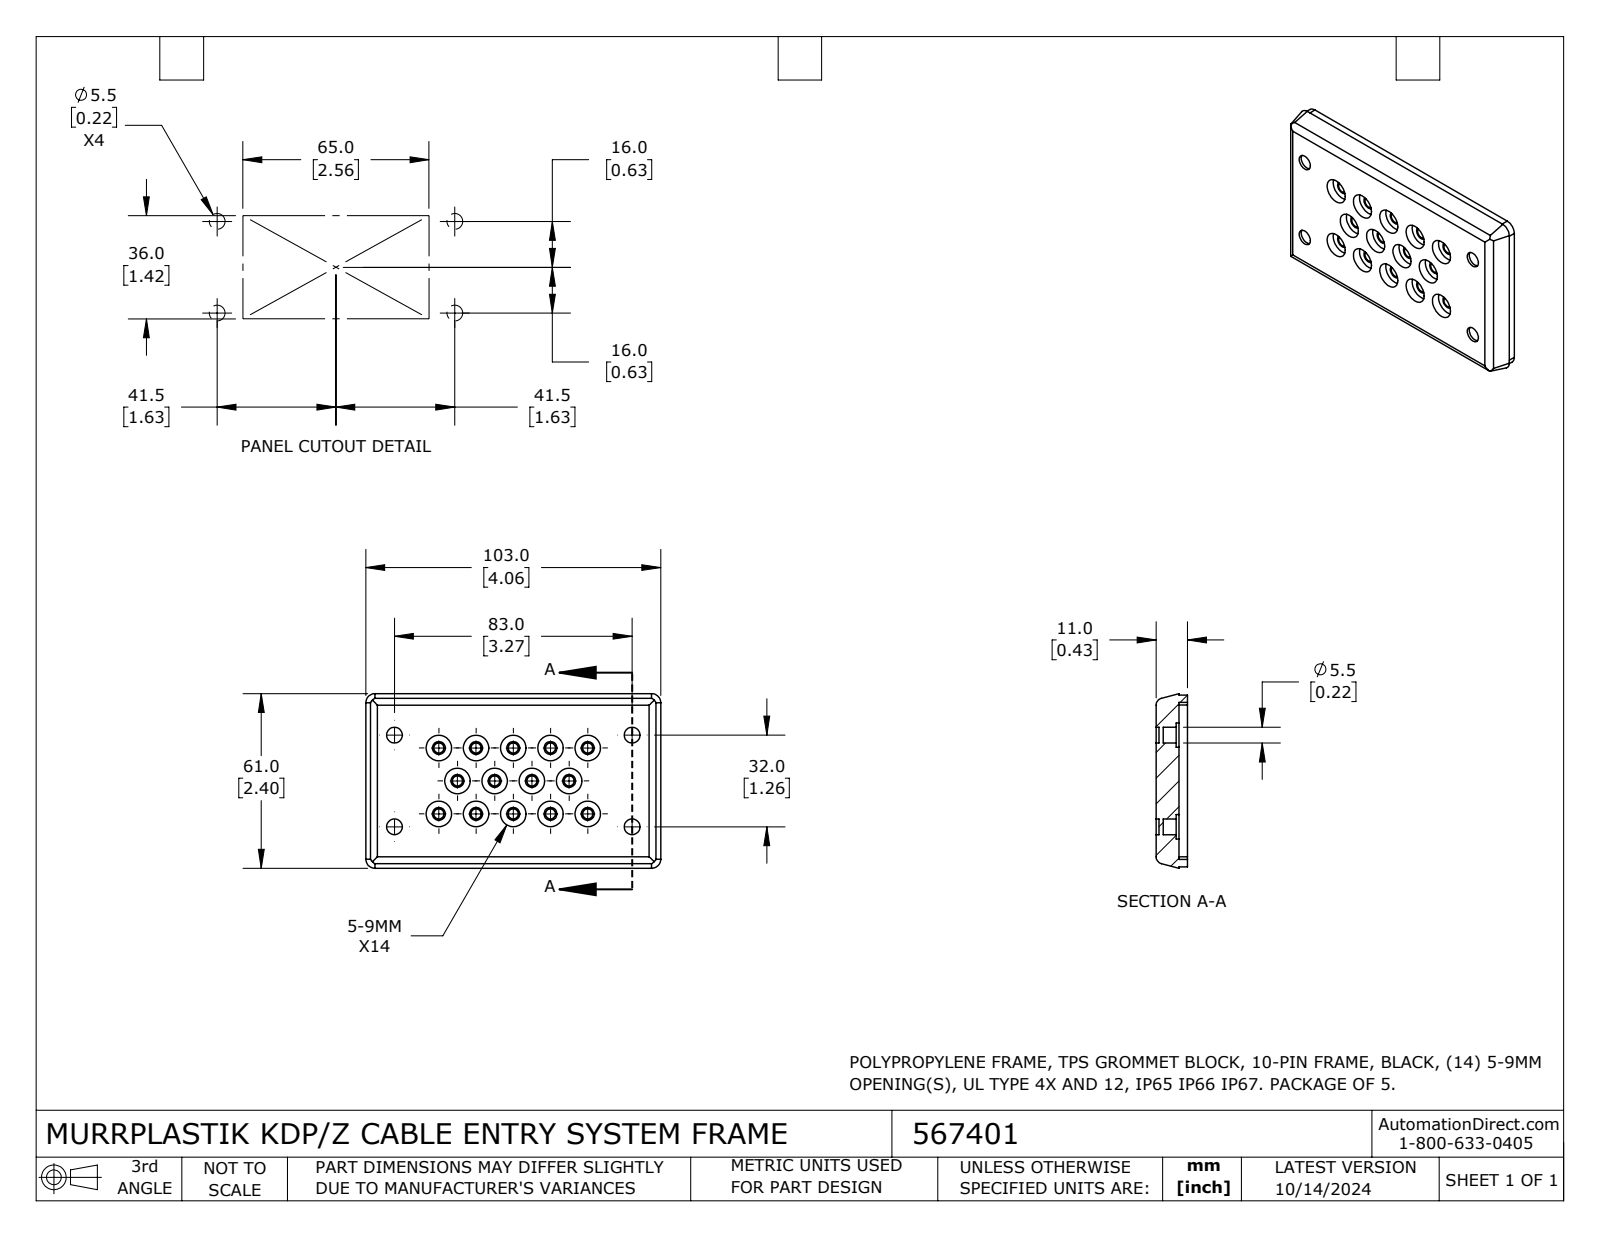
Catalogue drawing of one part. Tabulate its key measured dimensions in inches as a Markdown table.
| quantity | value |
| --- | --- |
| part name | 567401 |
| STEP written by | SolidWorks 2023 (CONFIG_CONTROL_DESIGN) |
| units | inches |
| bodies | 1 solid, 226 faces (84 planar, 138 cylindrical, 4 other) |
| overall size | 4.055 × 2.402 × 0.433 |
| volume | 2.306 in³ |
| surface area | 31.46 in² |
| round holes (diameter × count) | 0.177 × 14, 0.35 × 14, 0.217 × 4, 0.335 × 4 |
| round bosses / shafts (diameter × count) | 0.138 × 14 |
| partial cylindrical surfaces (radius × count) | 0.012 × 8, 0.035 × 4, 0.098 × 4, 0.138 × 4, 0.244 × 4, 0.266 × 4 |
| main face-to-face distances | 0.217, 0.098, 0.315, 0.118, 0.433, 0.197, 0.102, 0.386, 1.976, 2.26 |
| hole center spacings | 0.52, 0.891, 0.512, 1.024, 1.04, 1.357, 1.367, 0.906 |
